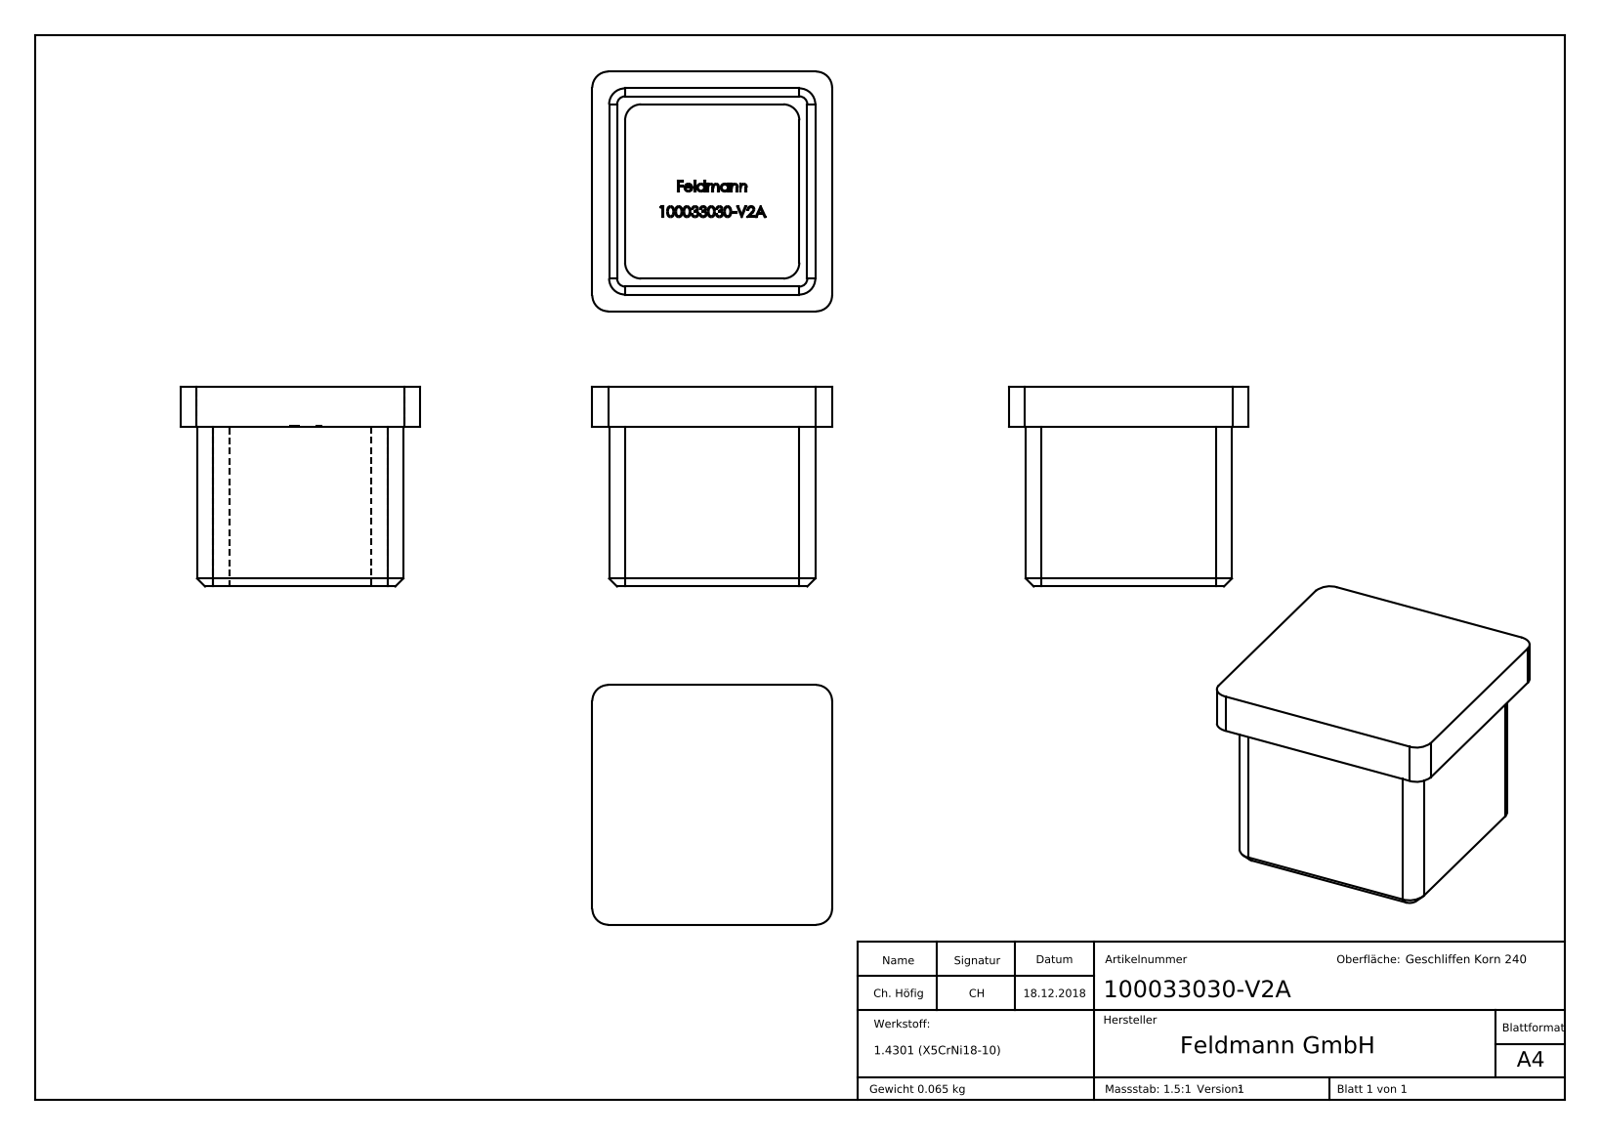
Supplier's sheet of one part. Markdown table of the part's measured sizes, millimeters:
| quantity | value |
| --- | --- |
| part name | 100033030-V2A |
| STEP written by | SolidWorks 2015 (CONFIG_CONTROL_DESIGN) |
| units | millimeters |
| bodies | 1 solid, 304 faces (147 planar, 12 cylindrical, 145 other) |
| overall size | 30 × 30 × 25 |
| volume | 8 241 mm³ |
| surface area | 5 999 mm² |
| partial cylindrical surfaces (radius × count) | 2 × 12 |
| main face-to-face distances | 2, 23.8, 25.8, 21.8, 5, 2.1, 4.1, 25.9, 27.9, 30 |
